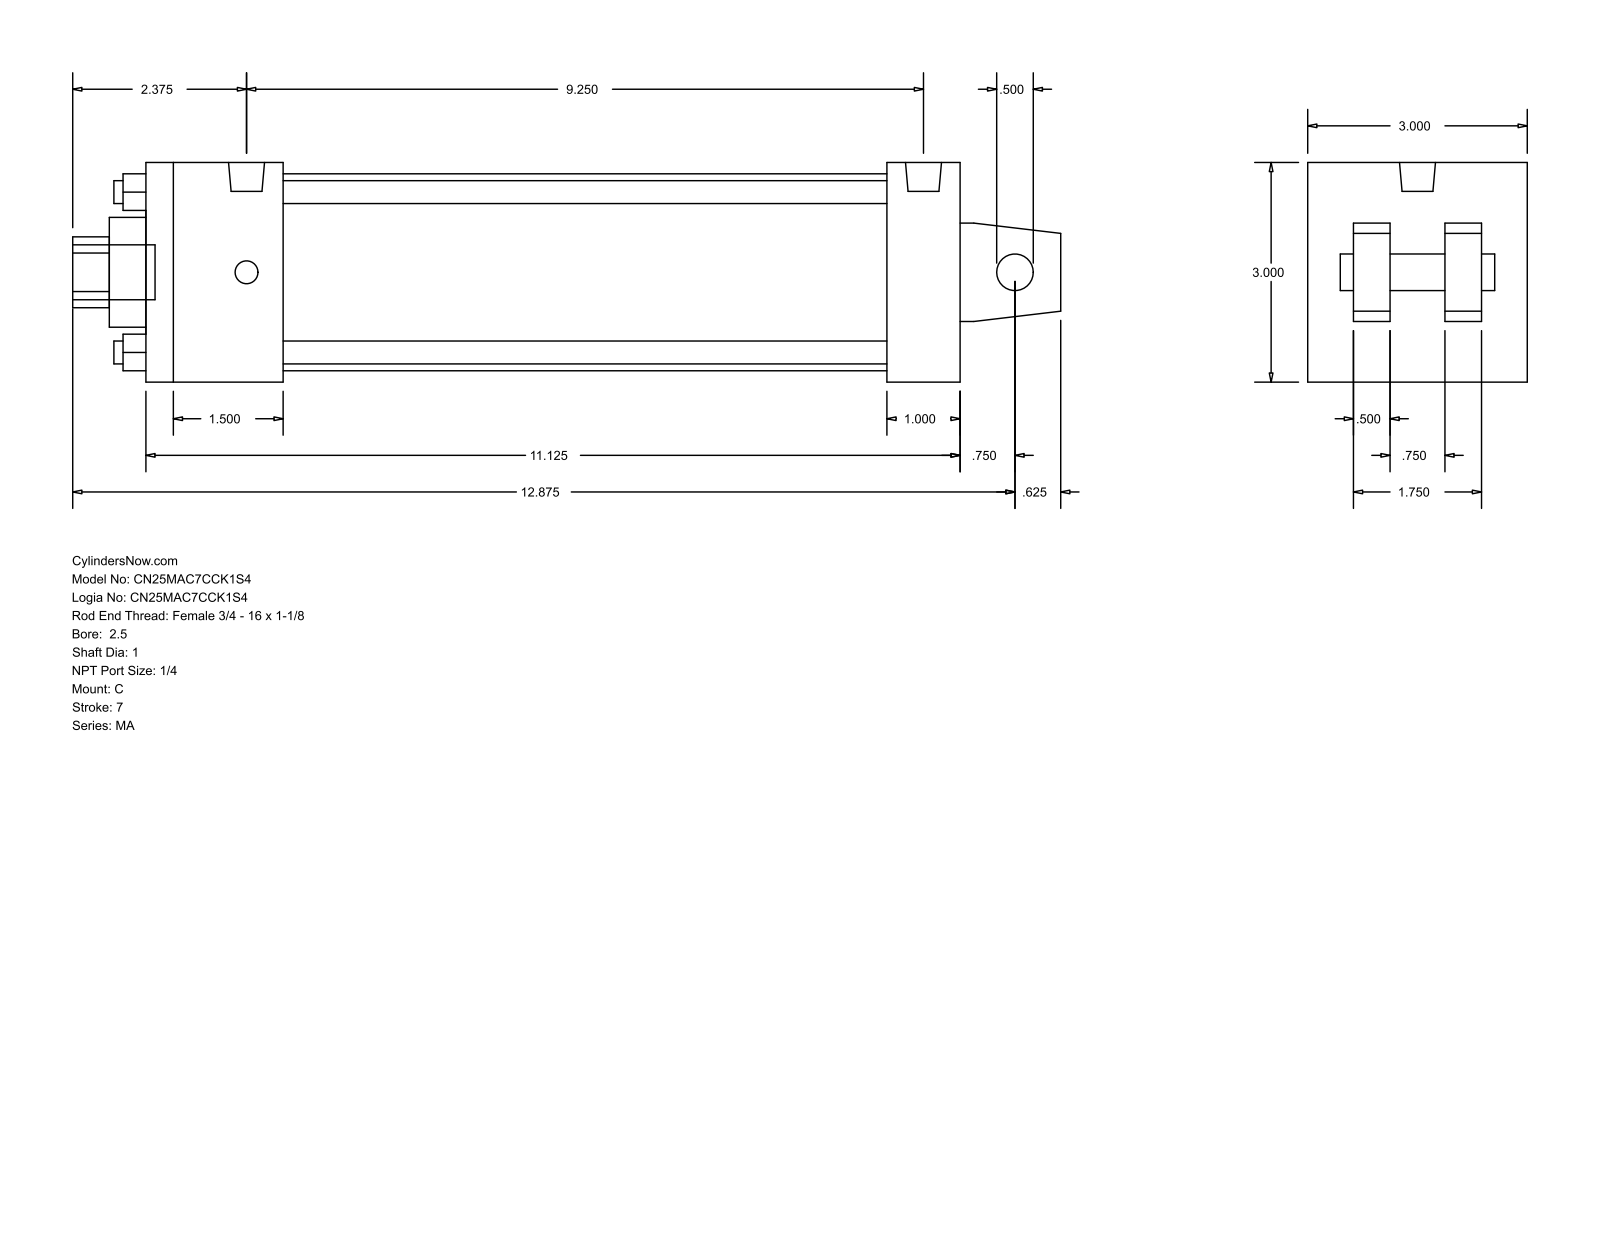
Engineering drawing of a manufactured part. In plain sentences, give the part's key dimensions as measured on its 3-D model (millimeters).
The part is named "MA_C__0250_1". Its 3-D file was written by "GSSL Pune (CONFIG_CONTROL_DESIGN)". It is 0 solids with 103 faces: 76 planar, 27 cylindrical and 0 other. Overall it measures 342.9 by 76.2 by 76.2 millimeters. Round holes: 4 of diameter 7.94, 1 of diameter 12.7, 1 of diameter 25.4, 1 of diameter 38.1, 1 of diameter 68.33. Round bosses or shafts: 4 of diameter 7.94, 2 of diameter 12.49, 1 of diameter 19.05. Partial cylindrical surfaces (rounded edges, fillets, slot ends): 1 of radius 12.29. The main face-to-face distances are 76.2, 47.63, 282.58, 12.7, 60.33, 15.87, 28.57, 257.17, 209.54, 234.95. The hole center spacings are 39.33, 55.62, 78.66.
